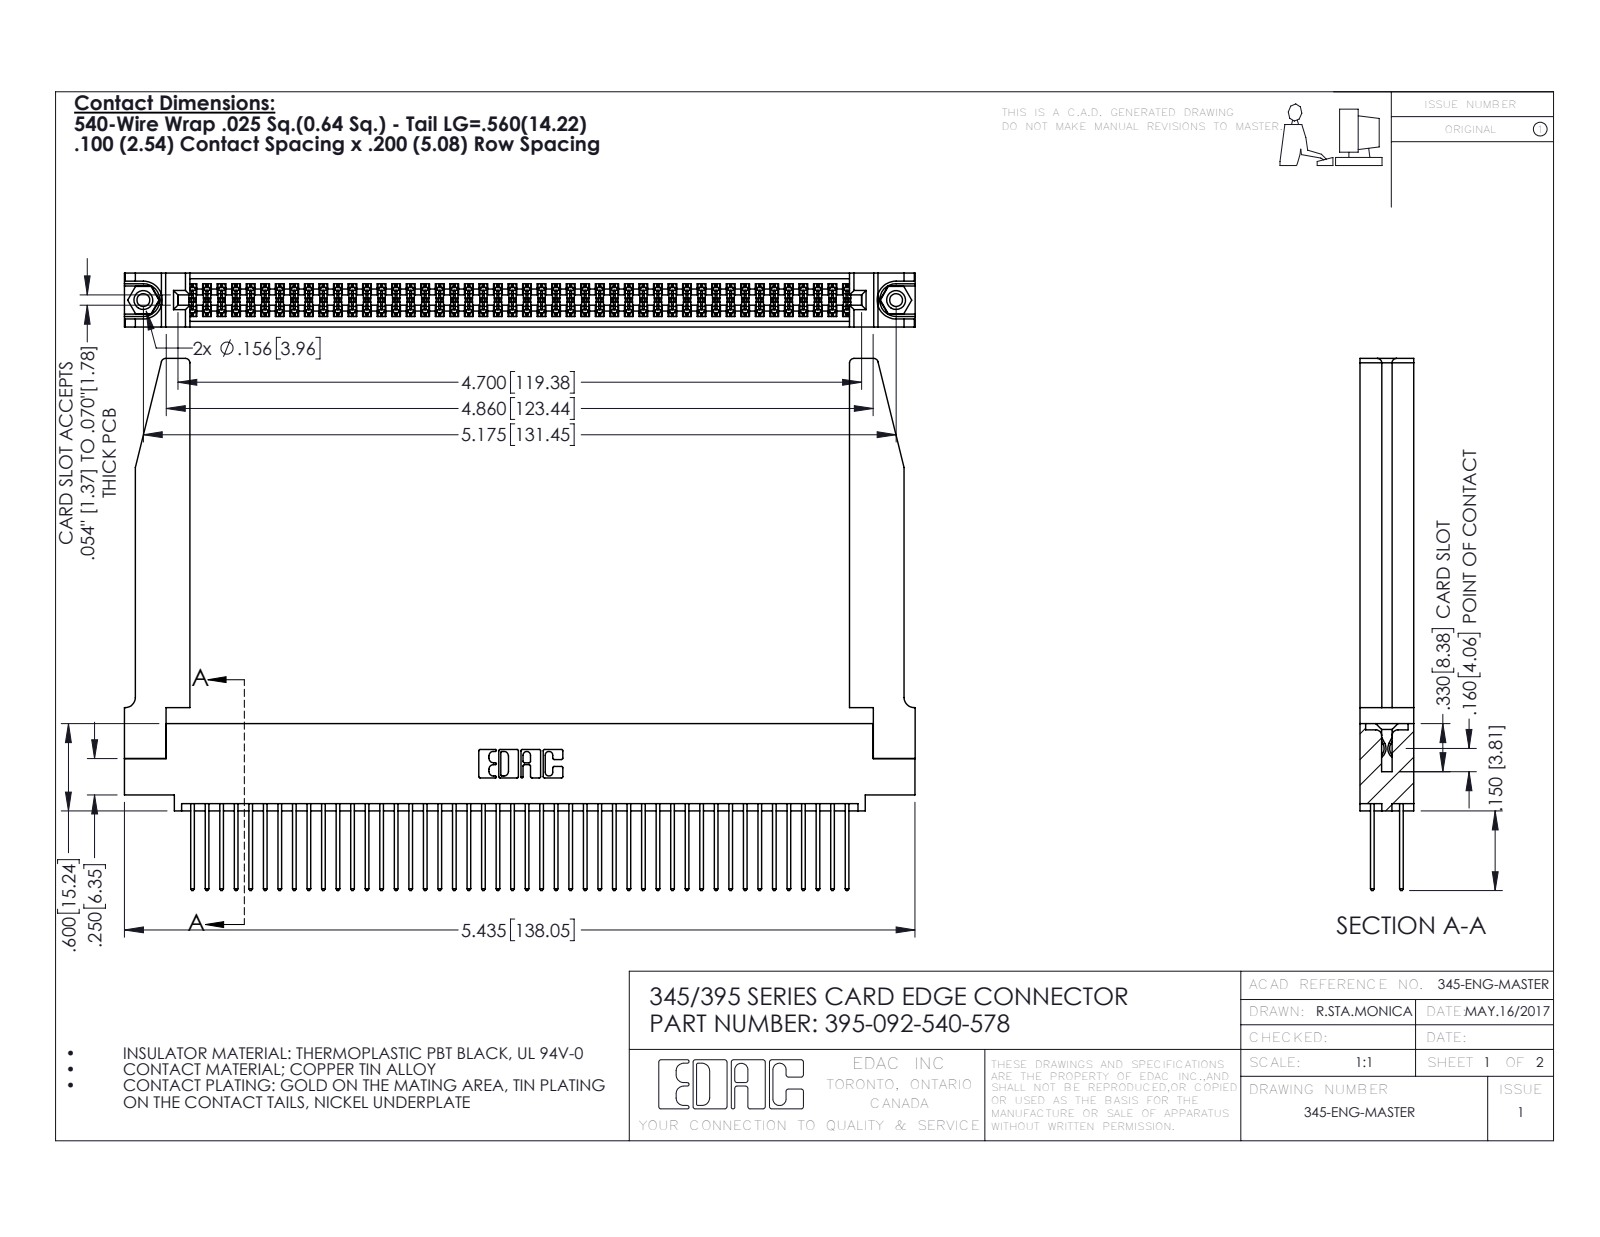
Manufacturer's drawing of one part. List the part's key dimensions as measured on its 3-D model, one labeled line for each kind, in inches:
Part name (STEP PRODUCT): 345-250-001_345-250-001-102; 345 Part_0.110 Offset - 0.156 Dia-TH; 345-292-001_345-293-140; 395-092-540-578 (+1 more)
STEP written by: SolidWorks 2016 (CONFIG_CONTROL_DESIGN)
Units: inches
Bodies: 97 solids, 4964 faces (3262 planar, 1650 cylindrical, 52 other)
Overall size (bounding box): 5.436 × 3.657 × 0.37
Volume: 1.312 in³ · Surface area: 44.82 in²
Round holes (diameter × count): ⌀0.089 ×2, ⌀0.125 ×2, ⌀0.156 ×2, ⌀0.064 ×1
Round bosses / shafts (diameter × count): ⌀0.155 ×2
Partial cylindrical surfaces — rounded edges, fillets, slot ends (radius × count): R0.006 ×138, R0.01 ×92, R0.01 ×22, R0.03 ×8, R0.007 ×6, R0.031 ×6, R0.026 ×3, R0.014 ×2
Main face-to-face distances: 0.072, 0.298, 0.37, 0.2, 0.098, 0.272, 0.025, 0.225, 0.175, 0.148
Hole centre spacings: 0.27, 4.939, 5.175
